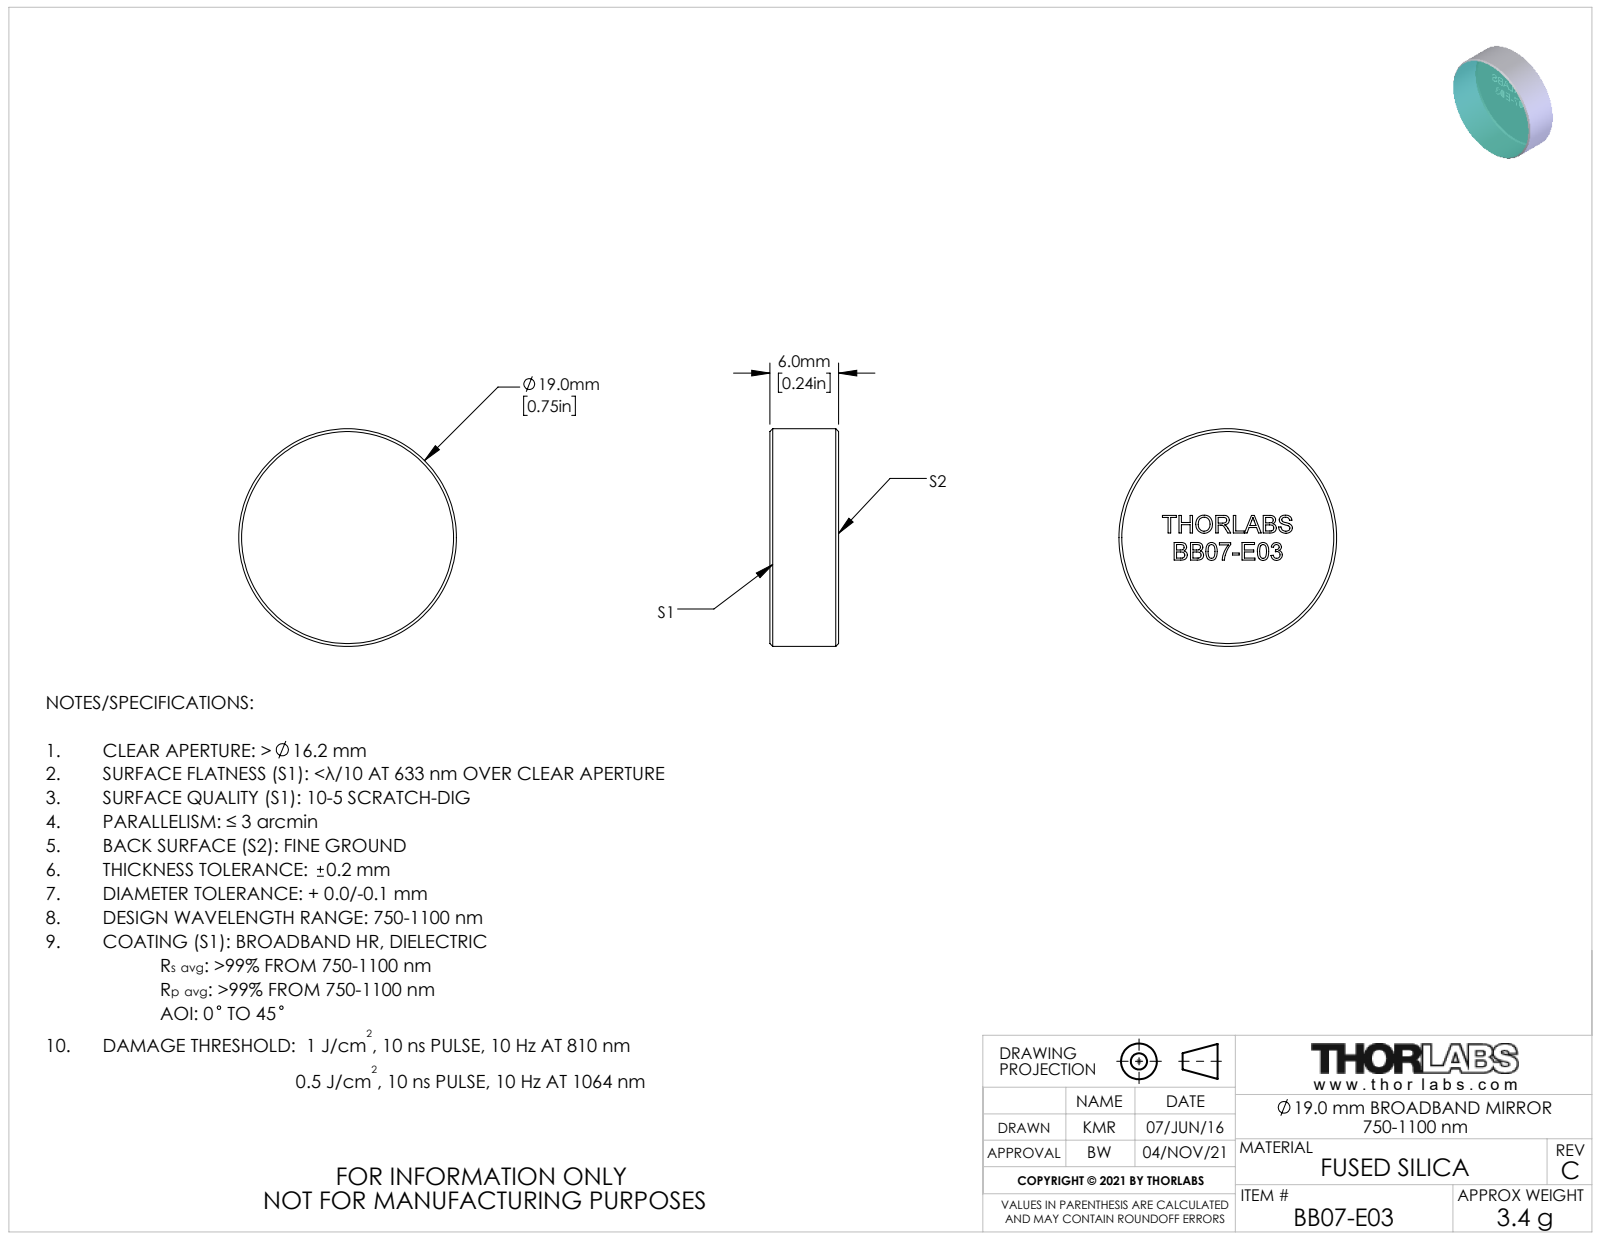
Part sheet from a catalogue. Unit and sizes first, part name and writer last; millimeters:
Units: millimetres
Overall size (bounding box): 19 × 19 × 6
Round bosses / shafts (diameter × count): ⌀19 ×1
Main face-to-face distances: 6, 1.54, 2.37, 1.36, 4.15, 1.92, 2.39, 3.2, 0.53, 0.83
Volume: 1 697 mm³ · Surface area: 908 mm²
Bodies: 1 solid, 235 faces (130 planar, 2 cylindrical, 103 other)
Part name (STEP PRODUCT): TTN024107-E0W
STEP written by: SolidWorks 2016 (CONFIG_CONTROL_DESIGN)
